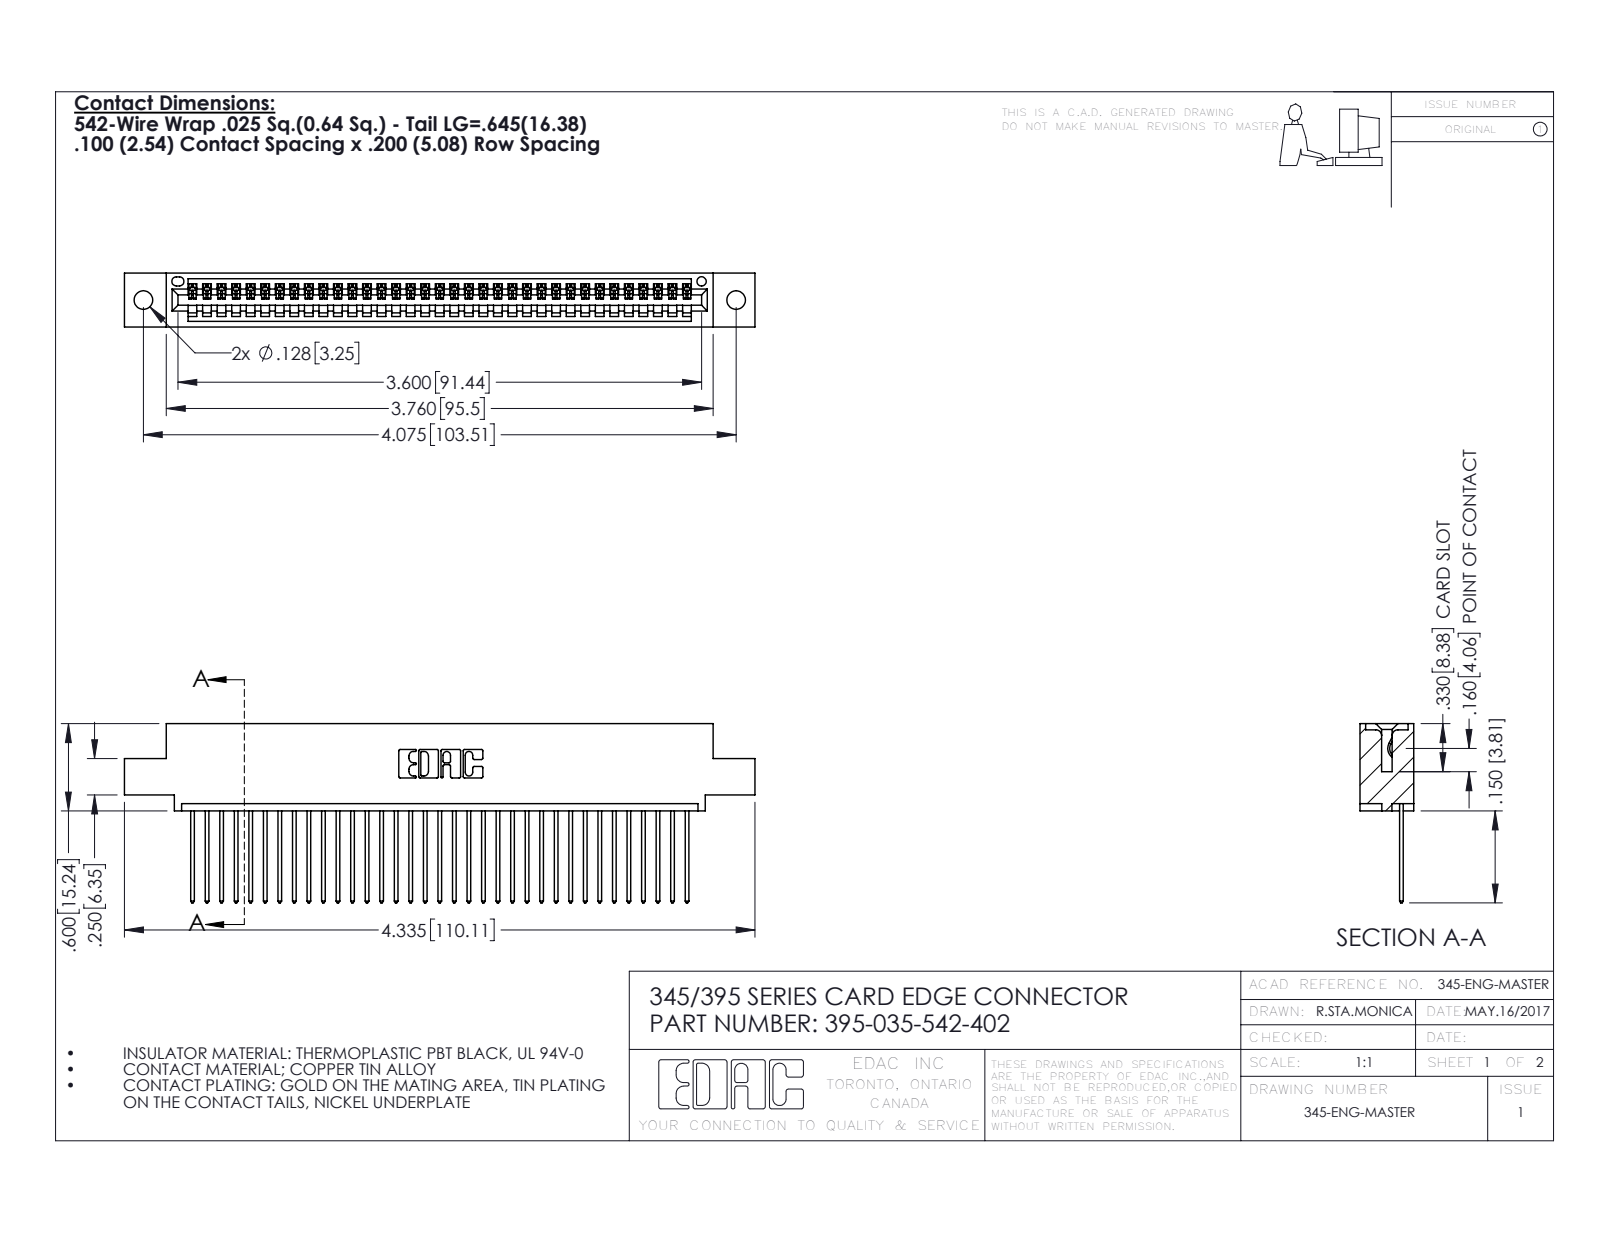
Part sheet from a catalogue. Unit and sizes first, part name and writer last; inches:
Units: inches
Overall size (bounding box): 4.335 × 1.232 × 0.37
Round holes (diameter × count): ⌀0.128 ×2, ⌀0.064 ×1
Partial cylindrical surfaces — rounded edges, fillets, slot ends (radius × count): R0.006 ×70, R0.01 ×70, R0.01 ×22, R0.007 ×6, R0.031 ×6, R0.026 ×3, R0.031 ×2, R0.04 ×2
Main face-to-face distances: 0.298, 0.072, 0.37, 0.098, 0.272, 0.025, 0.2, 0.225, 0.149, 0.072
Hole centre spacings: 0.27, 3.839, 4.075
Volume: 0.633 in³ · Surface area: 21.68 in²
Bodies: 36 solids, 2160 faces (1484 planar, 676 cylindrical, 0 other)
Part name (STEP PRODUCT): 345-292-001_345-293-142; 345 Part_0.110 Offset - 0.128 Dia; 395-035-542-402
STEP written by: SolidWorks 2016 (CONFIG_CONTROL_DESIGN)
